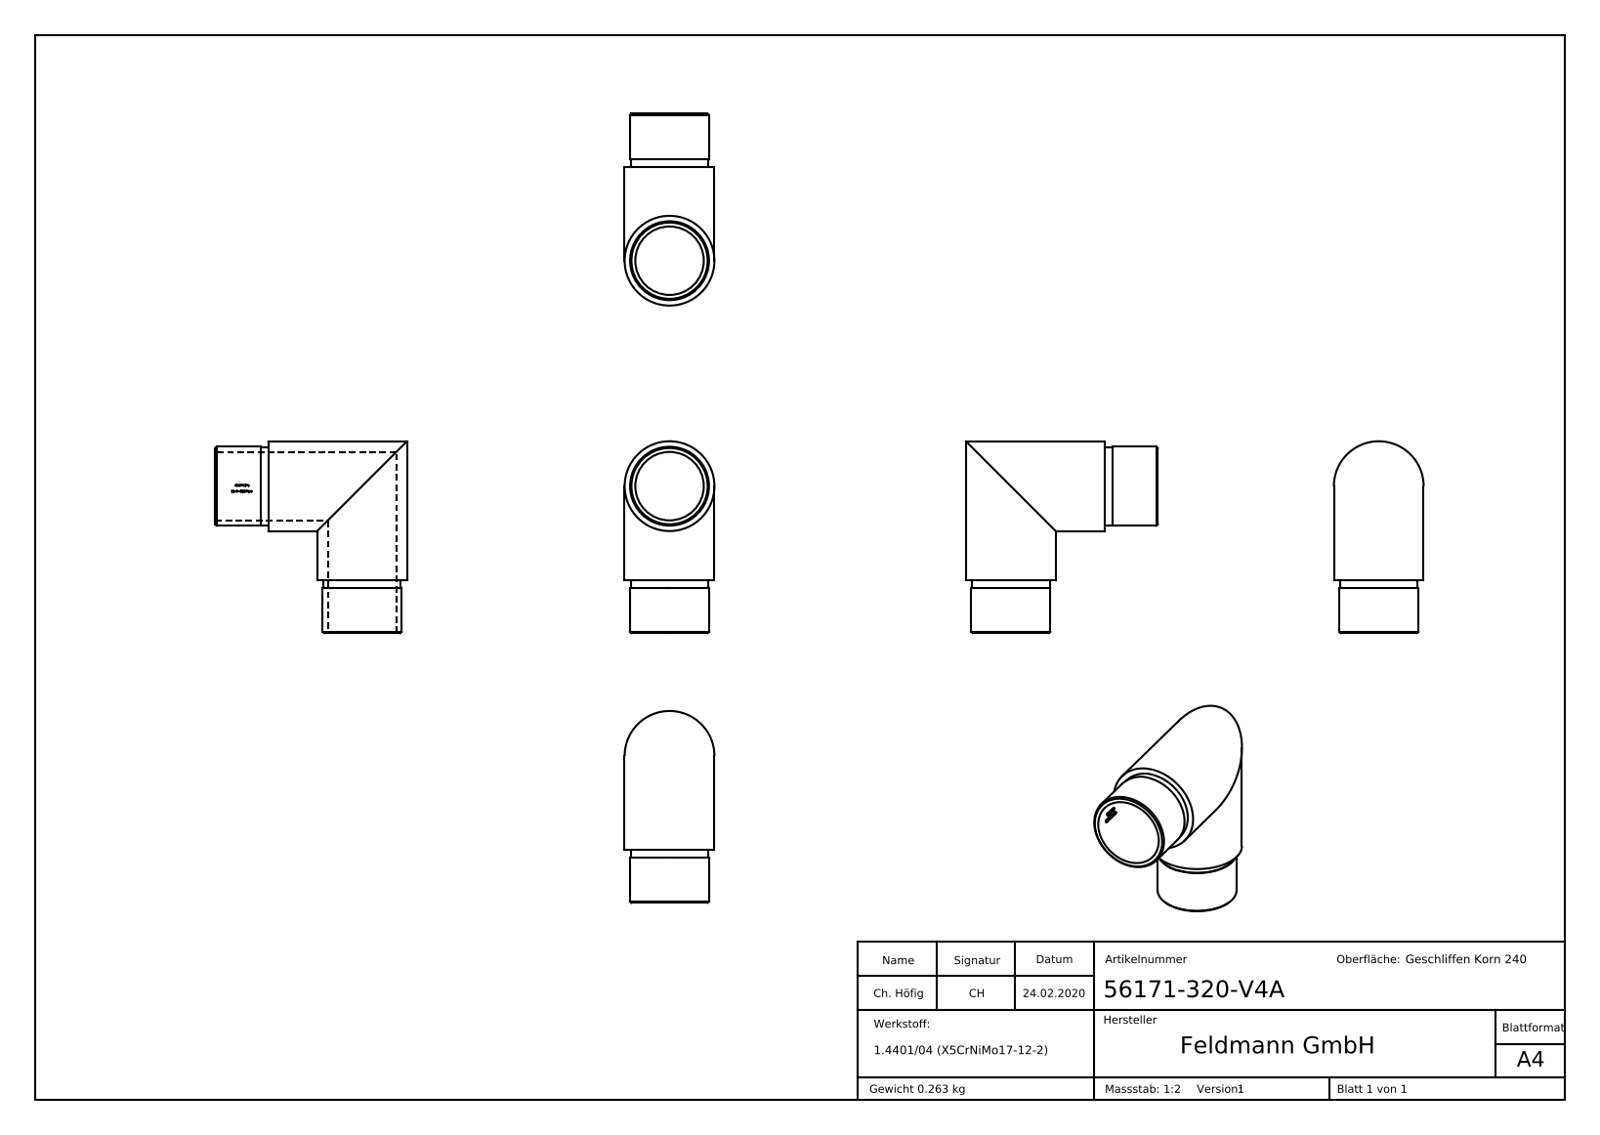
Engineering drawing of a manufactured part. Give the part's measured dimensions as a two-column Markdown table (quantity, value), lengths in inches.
| quantity | value |
| --- | --- |
| part name | 56171-320-V4A |
| STEP written by | SolidWorks 2015 (CONFIG_CONTROL_DESIGN) |
| units | inches |
| bodies | 1 solid, 267 faces (135 planar, 36 cylindrical, 96 other) |
| overall size | 2.835 × 2.835 × 1.327 |
| volume | 2.006 in³ |
| surface area | 32.29 in² |
| round holes (diameter × count) | 1.012 × 2 |
| round bosses / shafts (diameter × count) | 1.327 × 2, 1.165 × 2, 1.15 × 2 |
| partial cylindrical surfaces (radius × count) | 0.51 × 1 |
| main face-to-face distances | 0.787, 0.669, 0.118, 0.103, 0.033, 0.042, 0.031, 0.096, 0.039, 0.028 |
